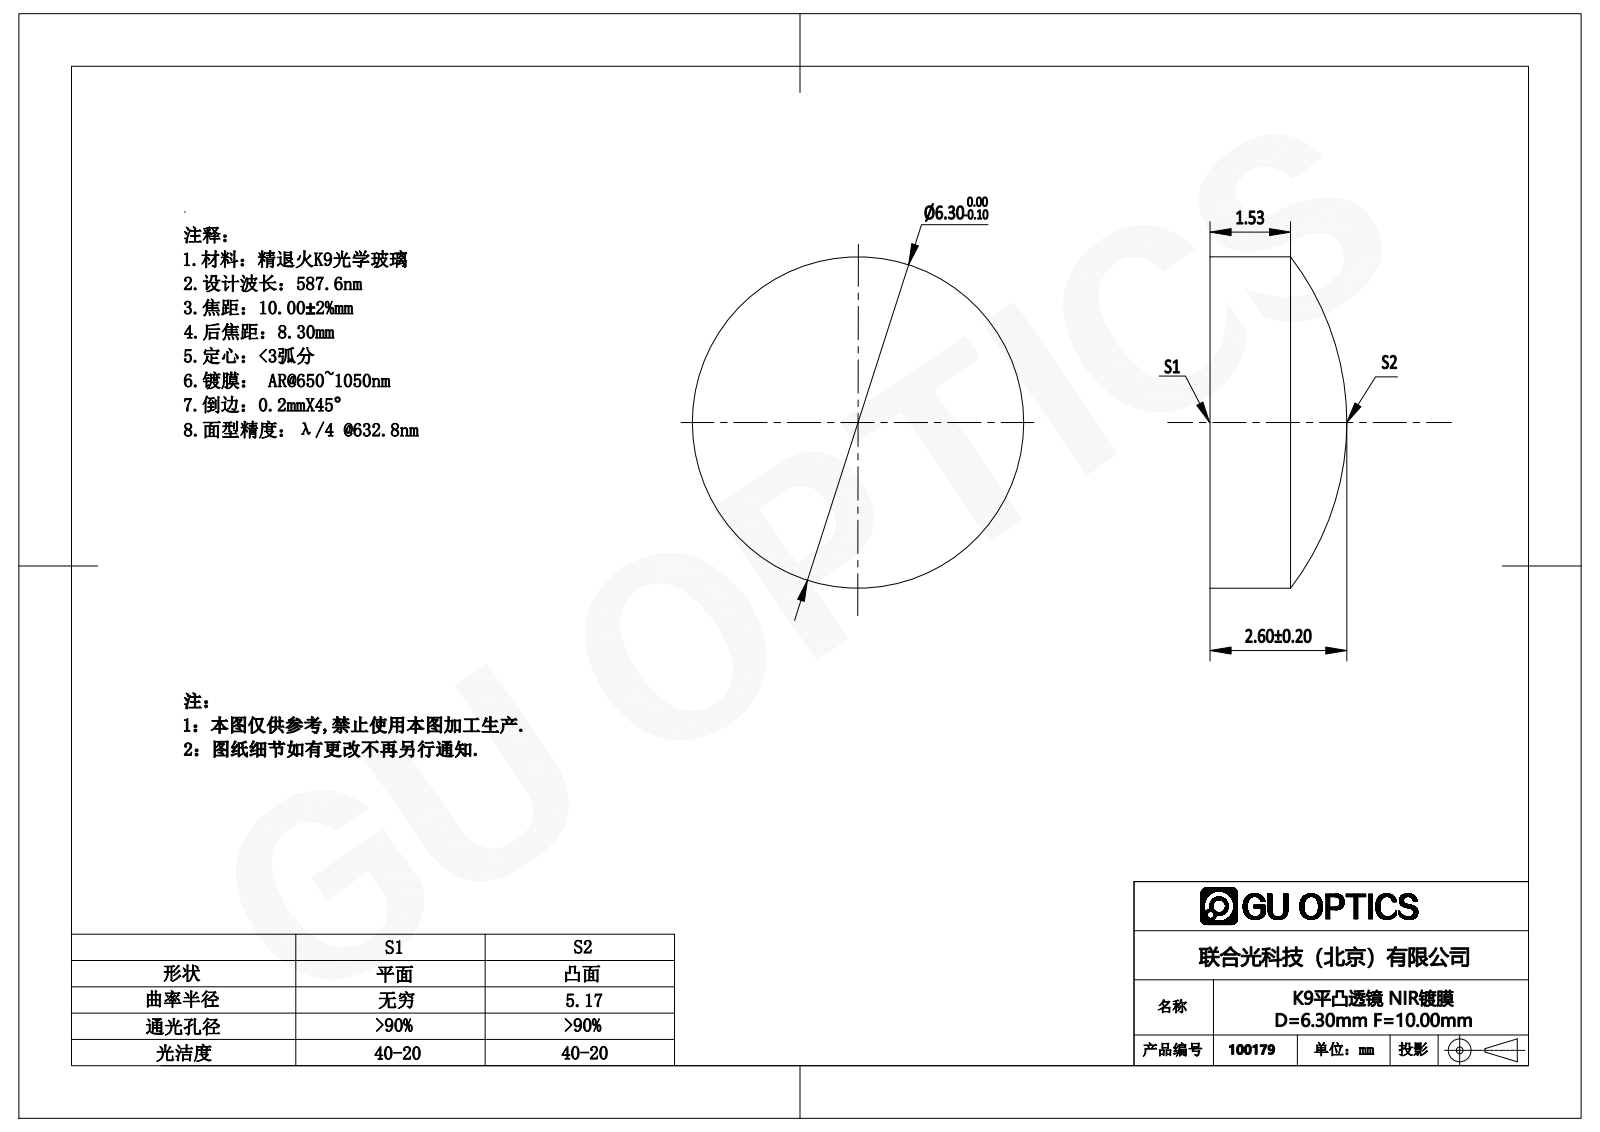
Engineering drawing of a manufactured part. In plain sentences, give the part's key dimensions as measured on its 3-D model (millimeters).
The part is named "100179". Its 3-D file was written by "SolidWorks 2016 (AUTOMOTIVE_DESIGN)". It is 1 solid with 5 faces: 1 planar, 2 cylindrical and 2 other. Overall it measures 6.3 by 6.3 by 2.6 millimeters. Its volume is 65 cubic millimeters and its surface area 96 square millimeters. Round bosses or shafts: 1 of diameter 6.3.
